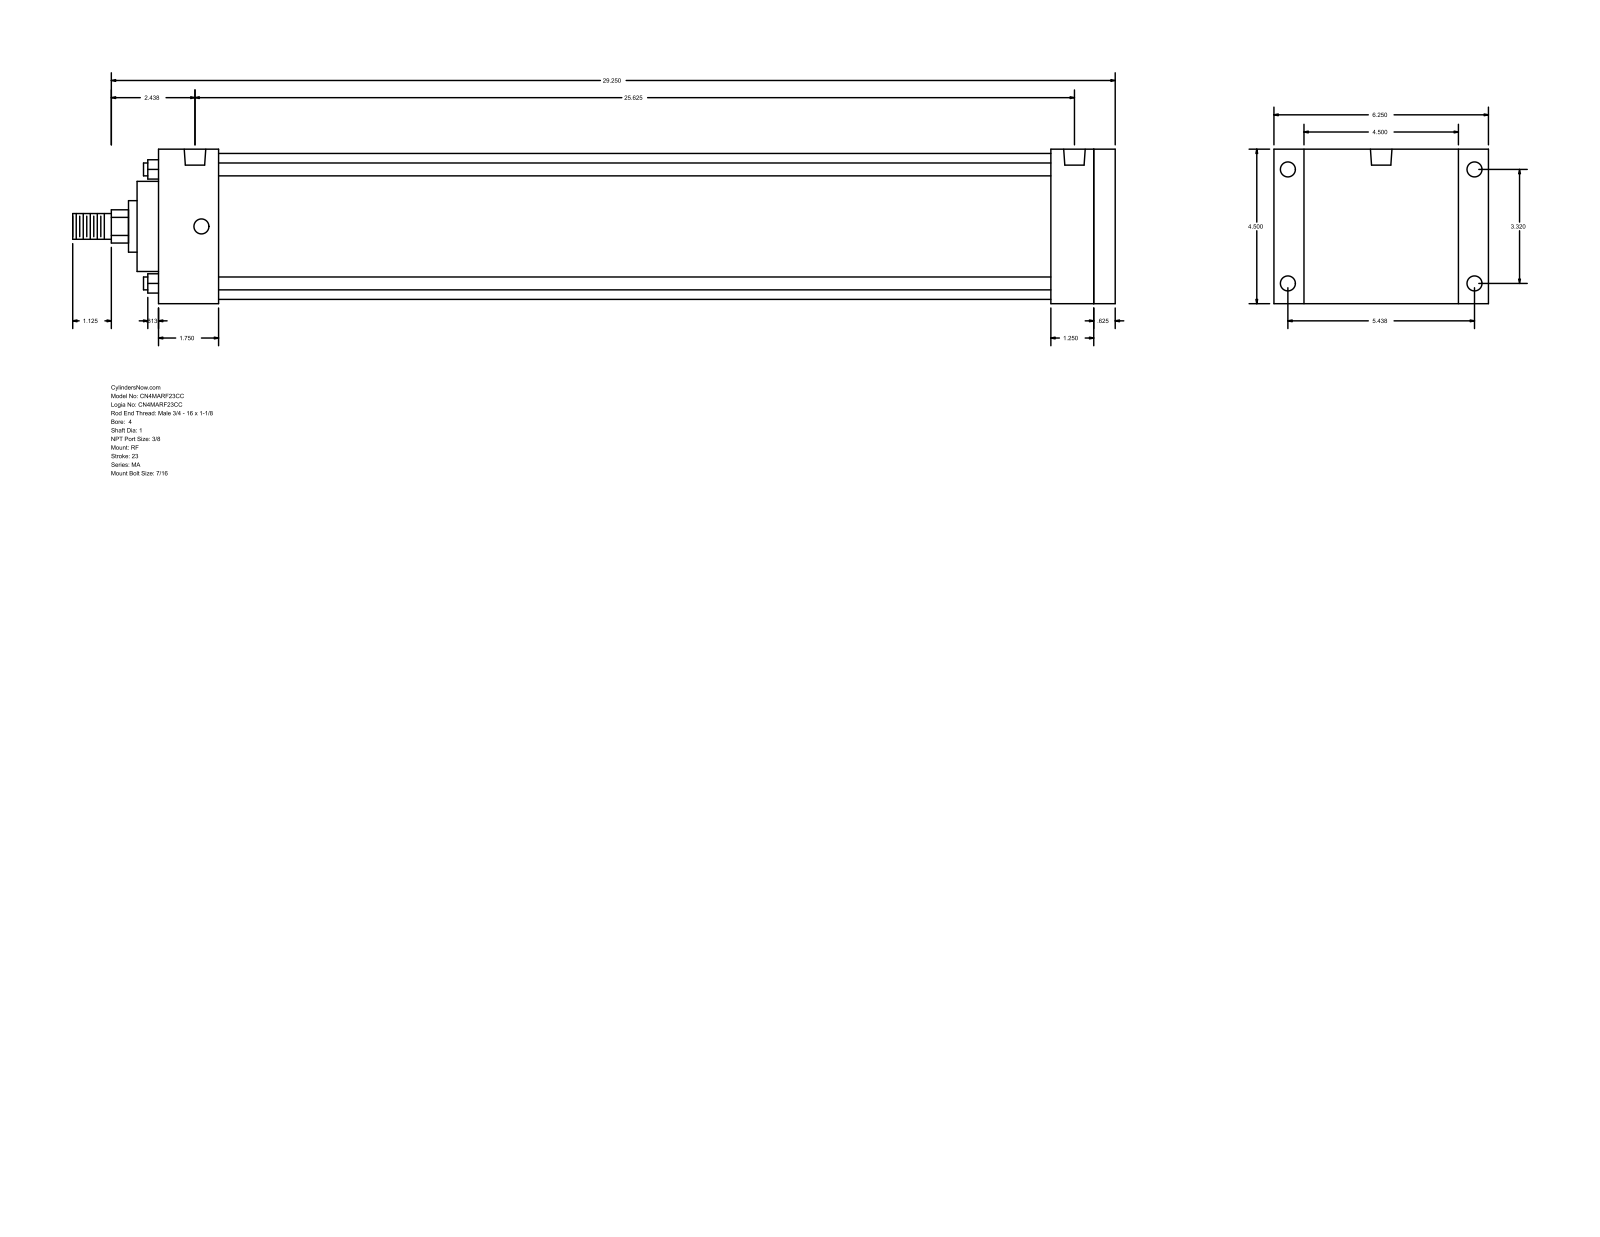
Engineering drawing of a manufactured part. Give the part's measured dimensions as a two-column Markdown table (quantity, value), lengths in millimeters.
| quantity | value |
| --- | --- |
| part name | MA_RF__0400_1 |
| STEP written by | GSSL Pune (CONFIG_CONTROL_DESIGN) |
| units | millimeters |
| bodies | 0 solids, 94 faces (65 planar, 29 cylindrical, 0 other) |
| overall size | 771.52 × 158.75 × 114.3 |
| round holes (diameter × count) | 11.11 × 8, 15.93 × 2 |
| round bosses / shafts (diameter × count) | 9.53 × 4, 107.95 × 1, 66.67 × 1, 38.1 × 1, 25.4 × 1, 19.05 × 1 |
| partial cylindrical surfaces (radius × count) | 12.29 × 1 |
| main face-to-face distances | 114.3, 708.03, 15.87, 692.16, 47.62, 22.23, 136.53, 660.41, 31.75, 44.46 |
| hole center spacings | 84.32, 138.12, 161.82, 641.35, 4.76, 4.77, 646.11, 646.12 |
